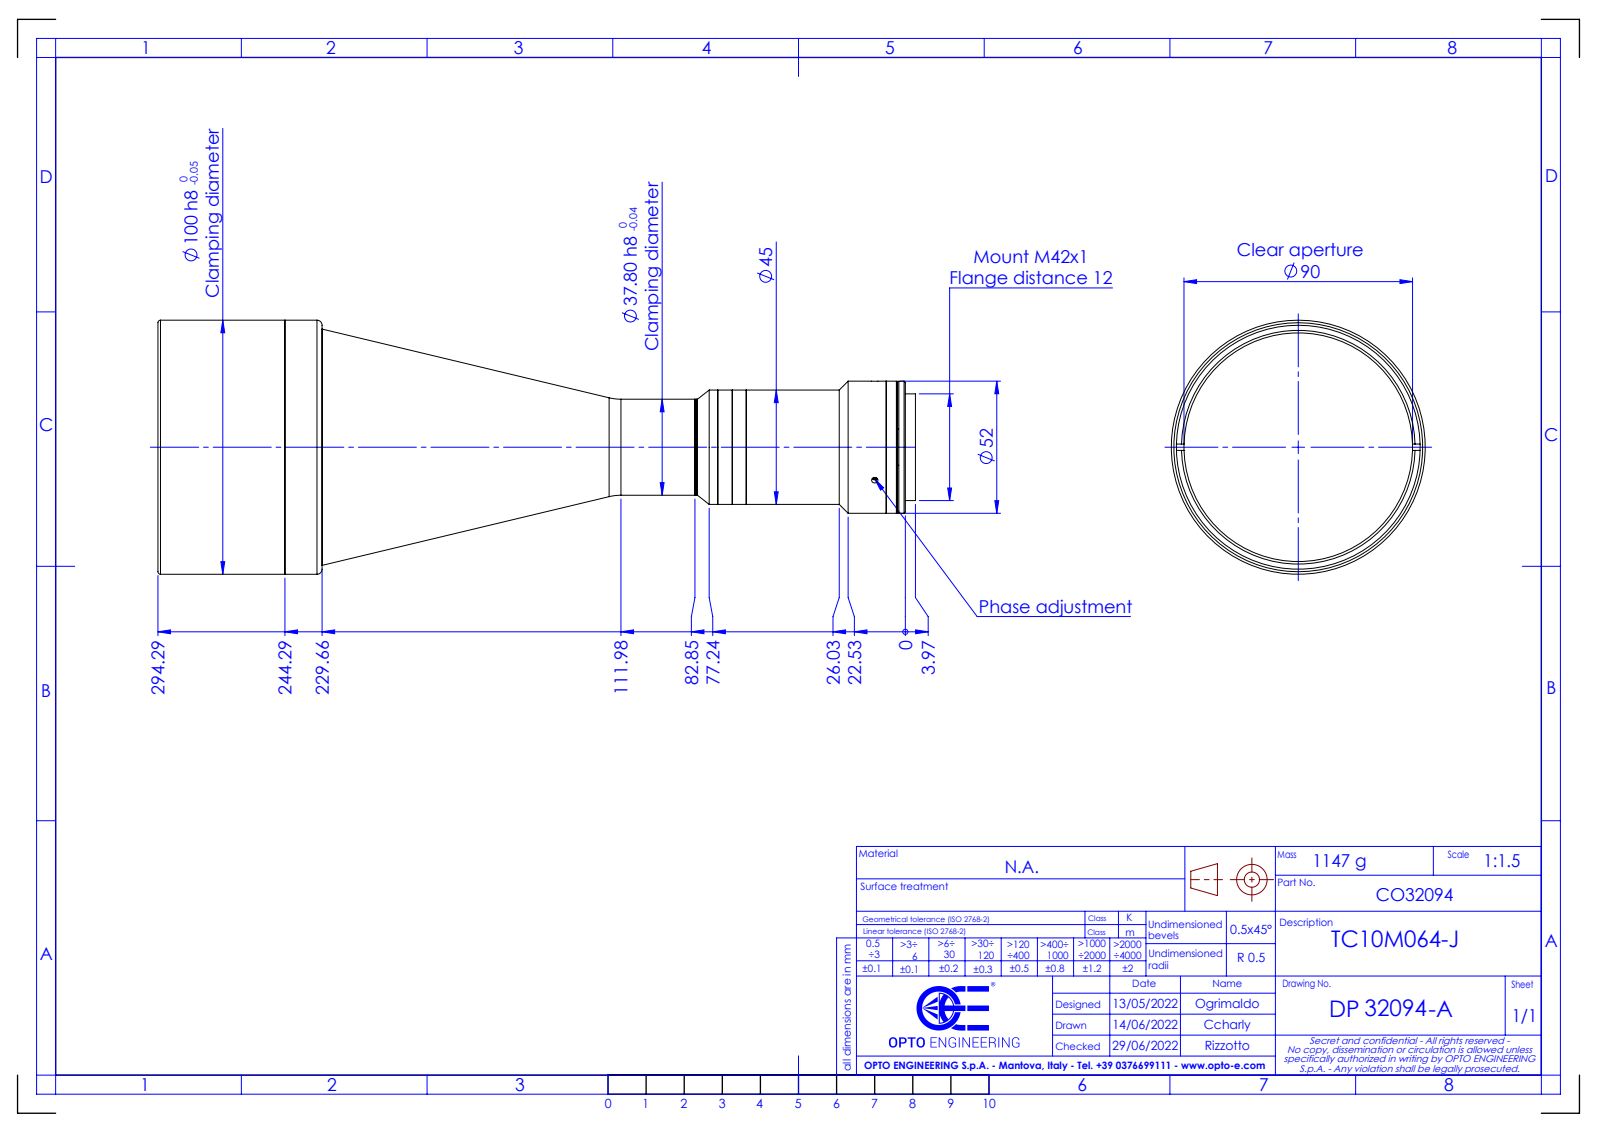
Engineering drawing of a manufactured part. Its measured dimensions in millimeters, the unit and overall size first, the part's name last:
Units: millimetres
Overall size (bounding box): 298.26 × 100 × 100
Round holes (diameter × count): ⌀2.5 ×3, ⌀38 ×1, ⌀41 ×1, ⌀90 ×1, ⌀96 ×1
Round bosses / shafts (diameter × count): ⌀100 ×1, ⌀93 ×1, ⌀52 ×1, ⌀51.8 ×1, ⌀45 ×1, ⌀42 ×1, ⌀37.8 ×1
Main face-to-face distances: 49.48, 291.21, 241.73, 290.24, 240.76, 0.97, 293.77, 244.29, 3.53, 2.56
Bodies: 0 solids, 96 faces (26 planar, 48 cylindrical, 22 other)
Part name (STEP PRODUCT): DP32094-A_TC10M064-J
STEP written by: SolidWorks 2021 (CONFIG_CONTROL_DESIGN)
